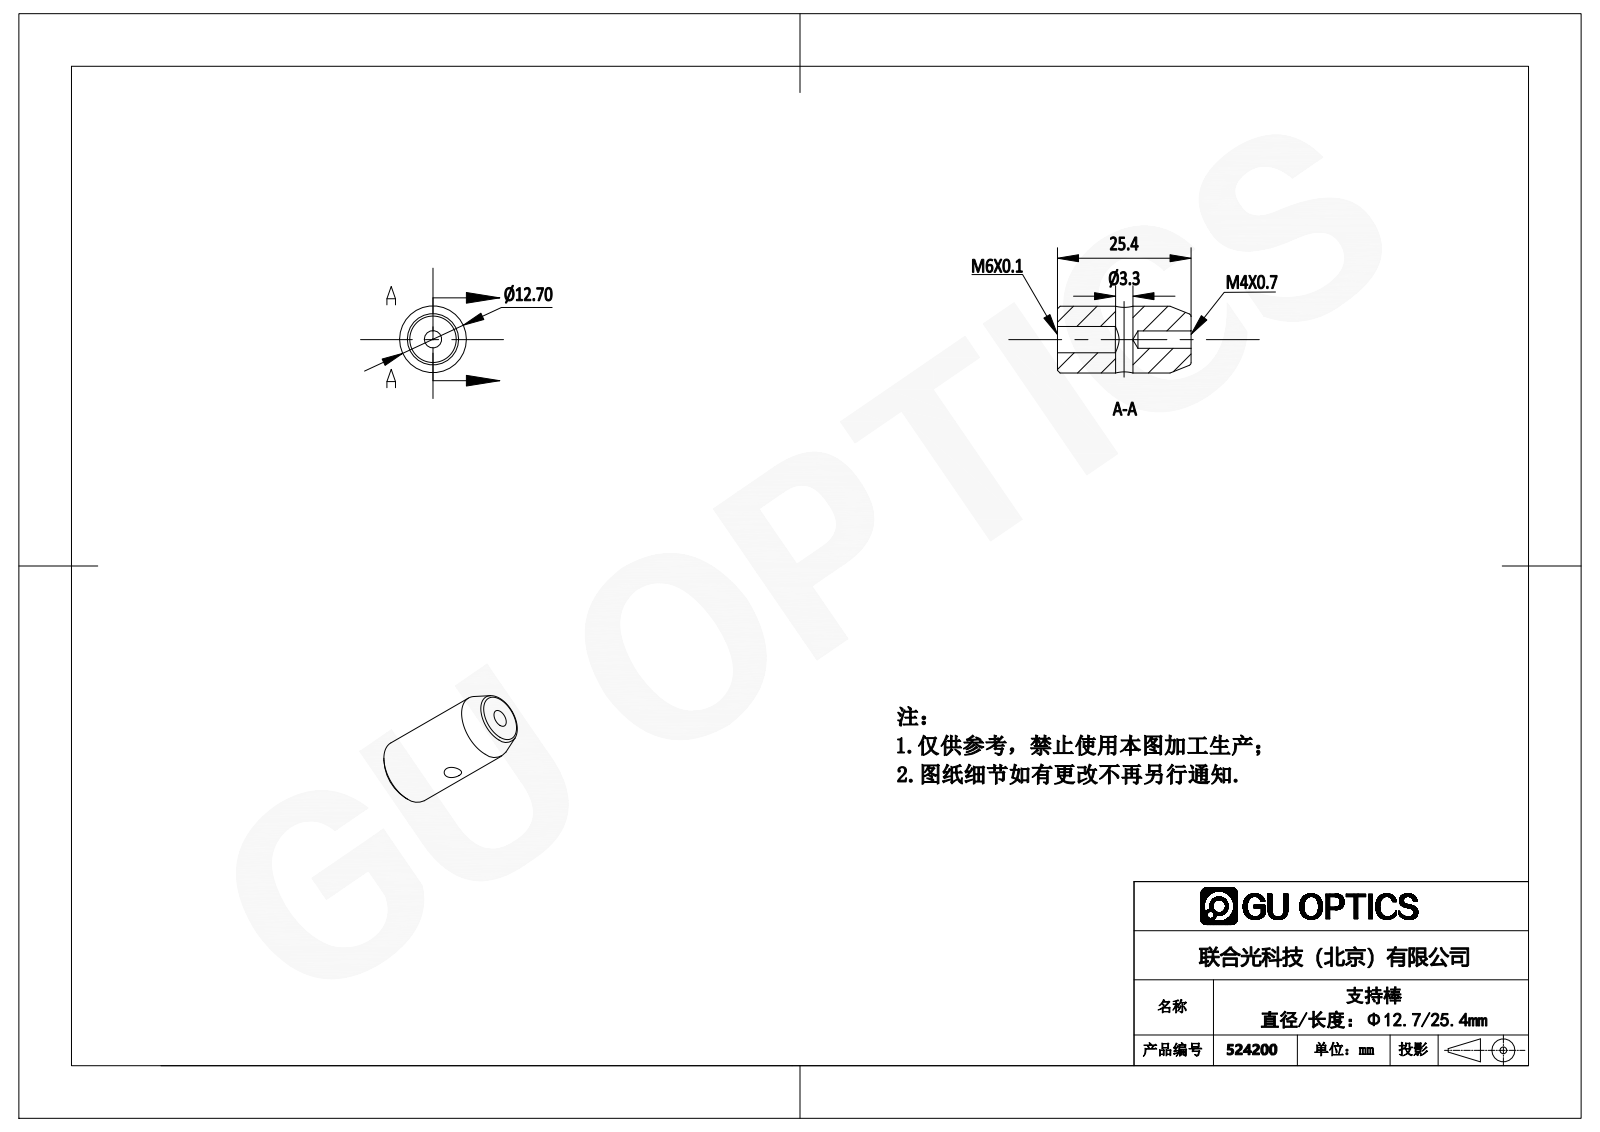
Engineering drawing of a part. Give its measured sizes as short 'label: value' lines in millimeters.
name: 524200
written by: SolidWorks 2016 (AUTOMOTIVE_DESIGN)
unit: mm
bodies: 1 solid, 20 faces (2 planar, 8 cylindrical, 10 other)
size: 25.4 × 12.7 × 12.7
volume: 2 678 mm³; area: 1 559 mm²
holes: 2× ⌀3.3, 1× ⌀5
bosses: 1× ⌀12.7
face distances: 25.4
